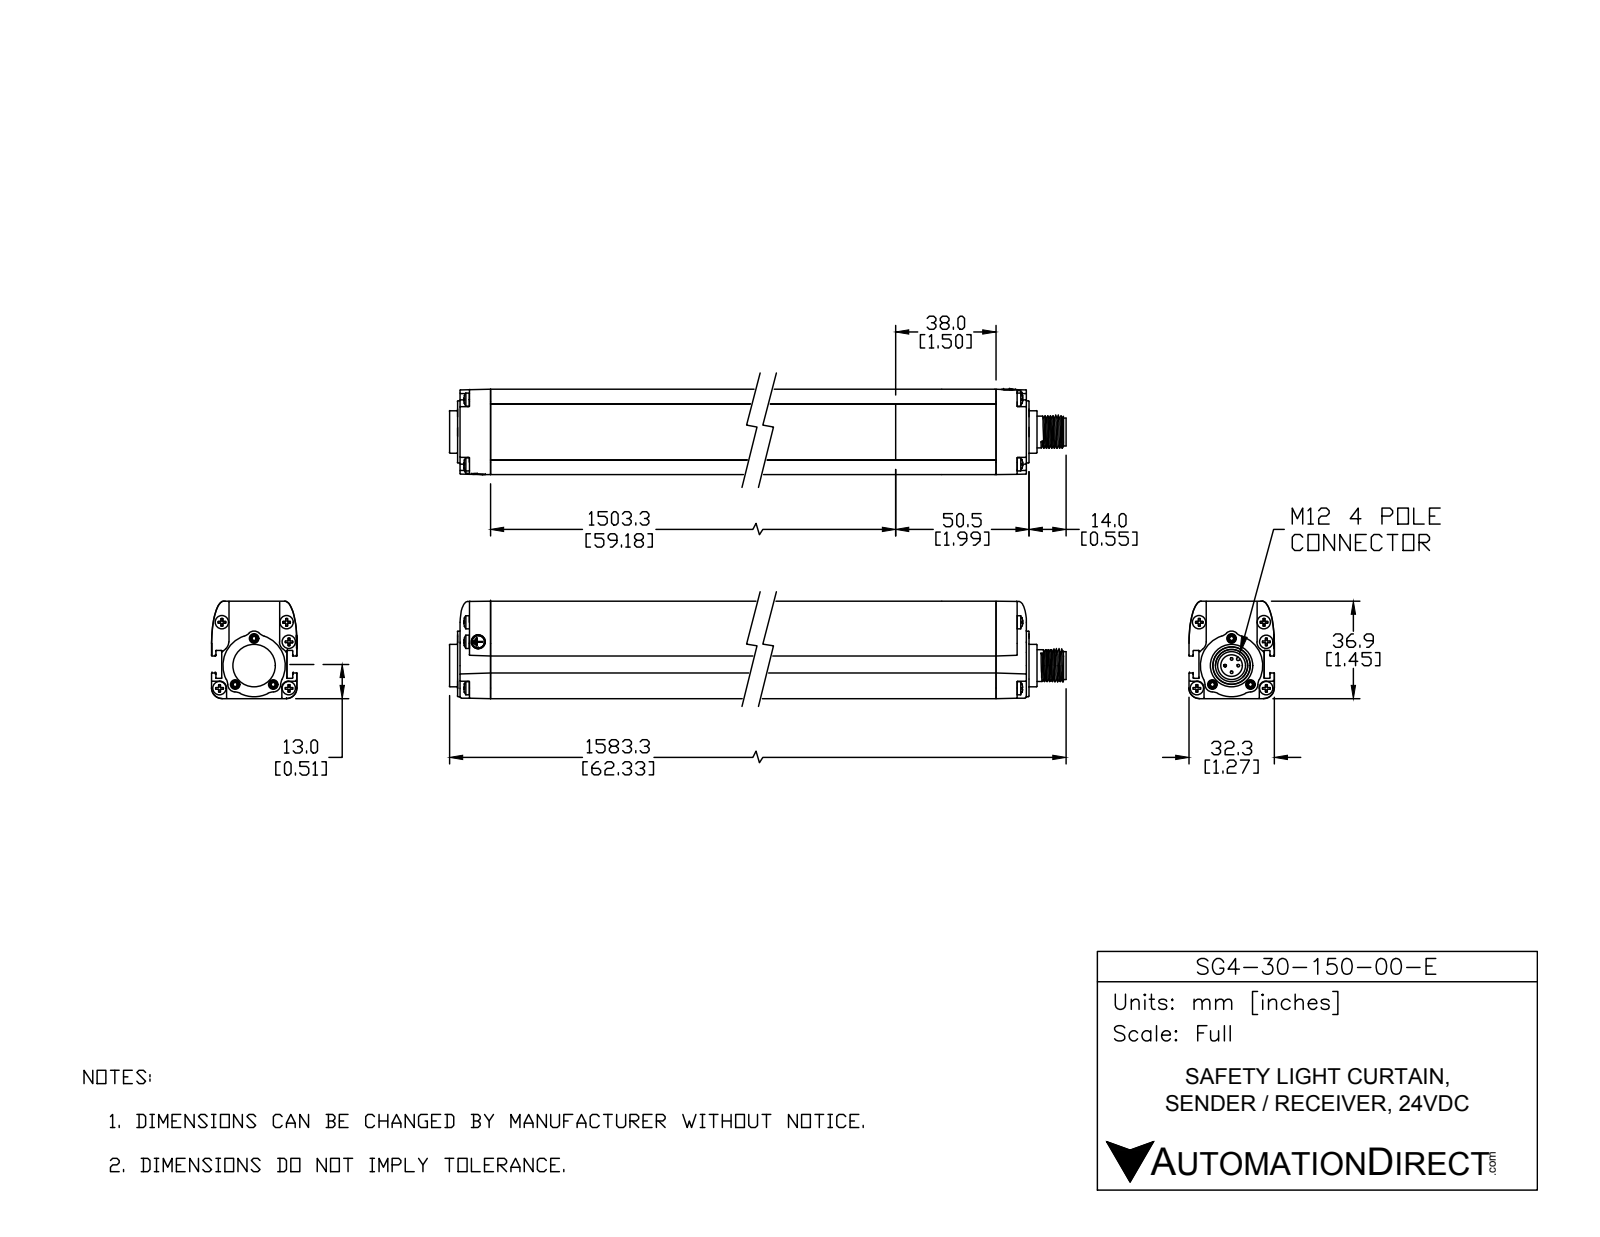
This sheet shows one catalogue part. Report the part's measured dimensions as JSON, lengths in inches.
{"part_name": "SG4-30-150-OO-E", "step_written_by": "SolidWorks 2017 (AUTOMOTIVE_DESIGN)", "units": "inches", "bodies": {"solids": 29, "faces": 1674, "planar": 410, "cylindrical": 591, "other": 673}, "overall_size": [62.335, 2.48, 2.055], "volume_in3": 99.47, "surface_area_in2": 591.7, "round_holes": [[0.106, 6], [0.209, 6], [0.081, 4], [0.165, 4], [0.26, 4], [0.059, 3], [0.142, 3], [0.323, 1], [0.376, 1], [0.433, 1], [0.563, 1]], "round_bosses_or_shafts": [[0.197, 10], [0.394, 4], [0.039, 4], [0.185, 2], [0.63, 1], [0.55, 1], [0.472, 1], [0.413, 1]], "partial_cylinders_radius": [[0.008, 148], [0.004, 120], [0.006, 18], [0.106, 18], [0.118, 8], [0.197, 7], [0.11, 3], [0.016, 2]], "face_to_face_distances": [0.079, 1.272, 1.429, 0.15, 1.122, 1.35, 0.157, 0.972, 0.333, 0.063], "hole_center_spacings": [0.569, 59.107, 0.402, 0.24, 0.293, 0.52, 0.541, 0.619]}
